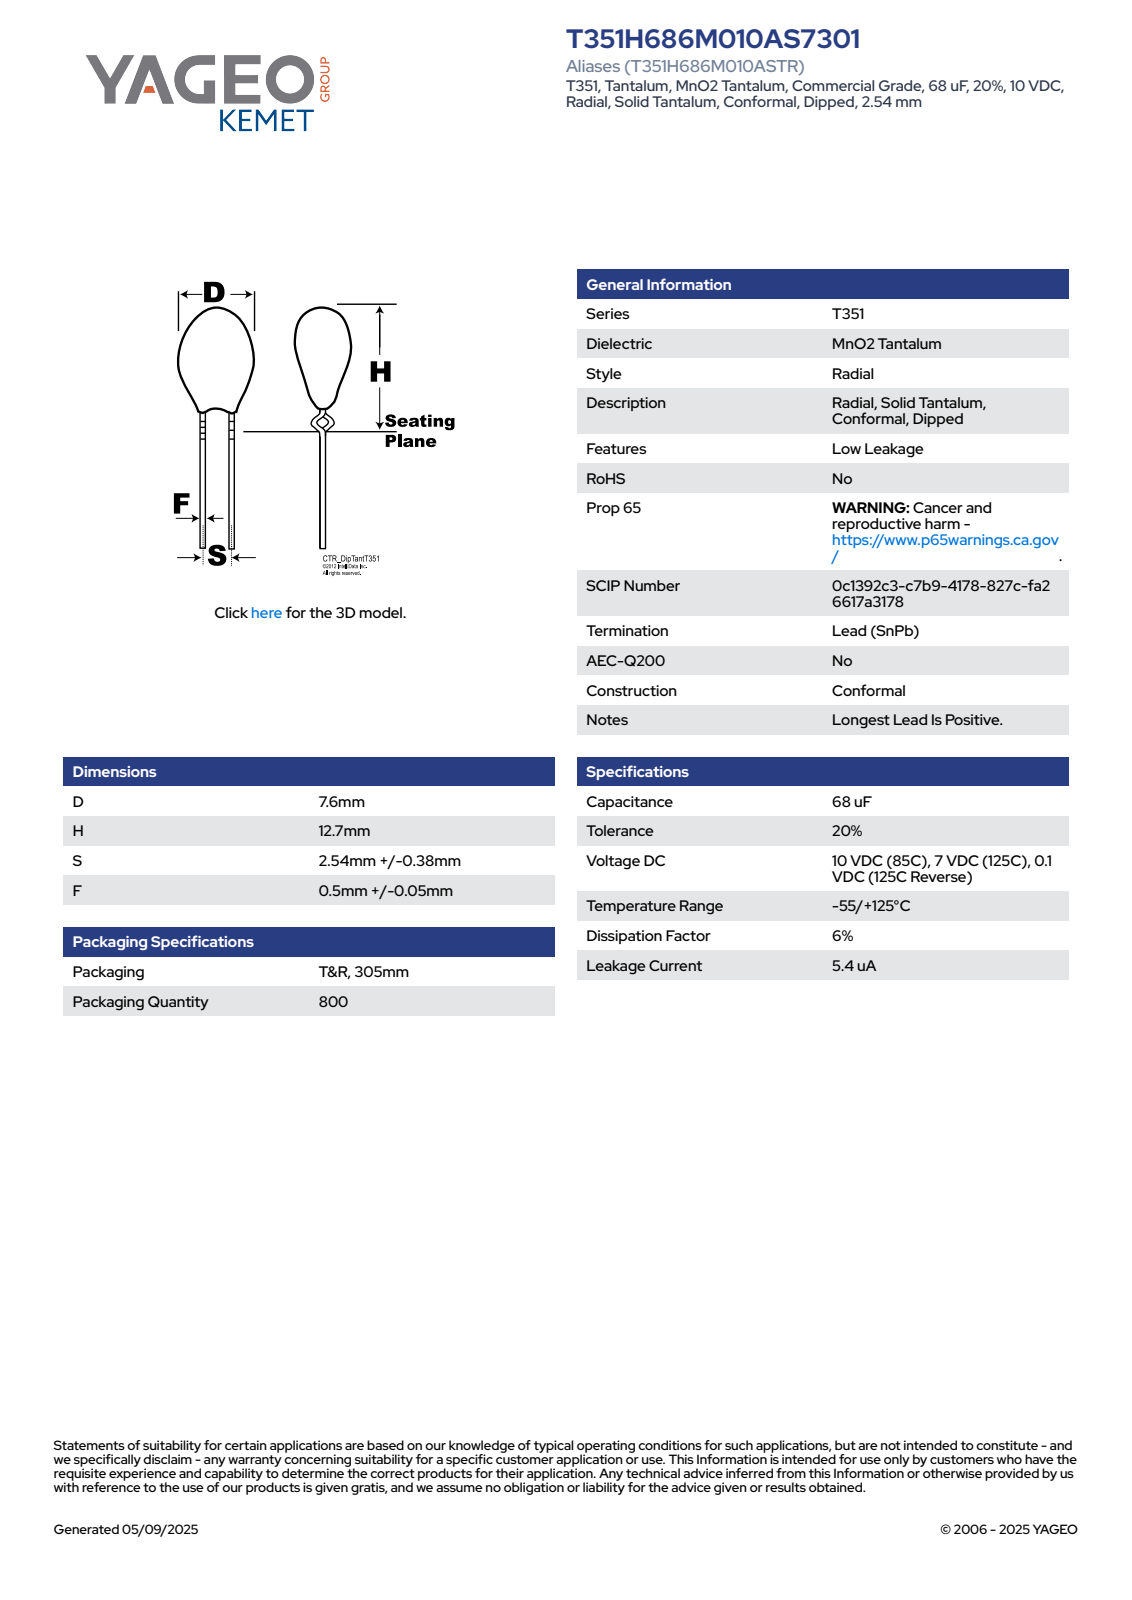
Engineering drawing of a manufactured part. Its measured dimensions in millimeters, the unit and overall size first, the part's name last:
Units: millimetres
Overall size (bounding box): 18.26 × 7.6 × 7.6
Round bosses / shafts (diameter × count): ⌀0.55 ×2, ⌀7.6 ×1
Partial cylindrical surfaces — rounded edges, fillets, slot ends (radius × count): R3.79 ×1
Main face-to-face distances: 9, 13.79, 4.79, 12.99, 3.99, 0.8, 0.35, 0.65, 0.5, 13.14
Volume: 317 mm³ · Surface area: 262 mm²
Bodies: 1 solid, 88 faces (27 planar, 10 cylindrical, 51 other)
Part name (STEP PRODUCT): CTR_T351_D7.6H12.7S2.54LL5.56F0.55
STEP written by: SolidWorks 2014 (AUTOMOTIVE_DESIGN)
